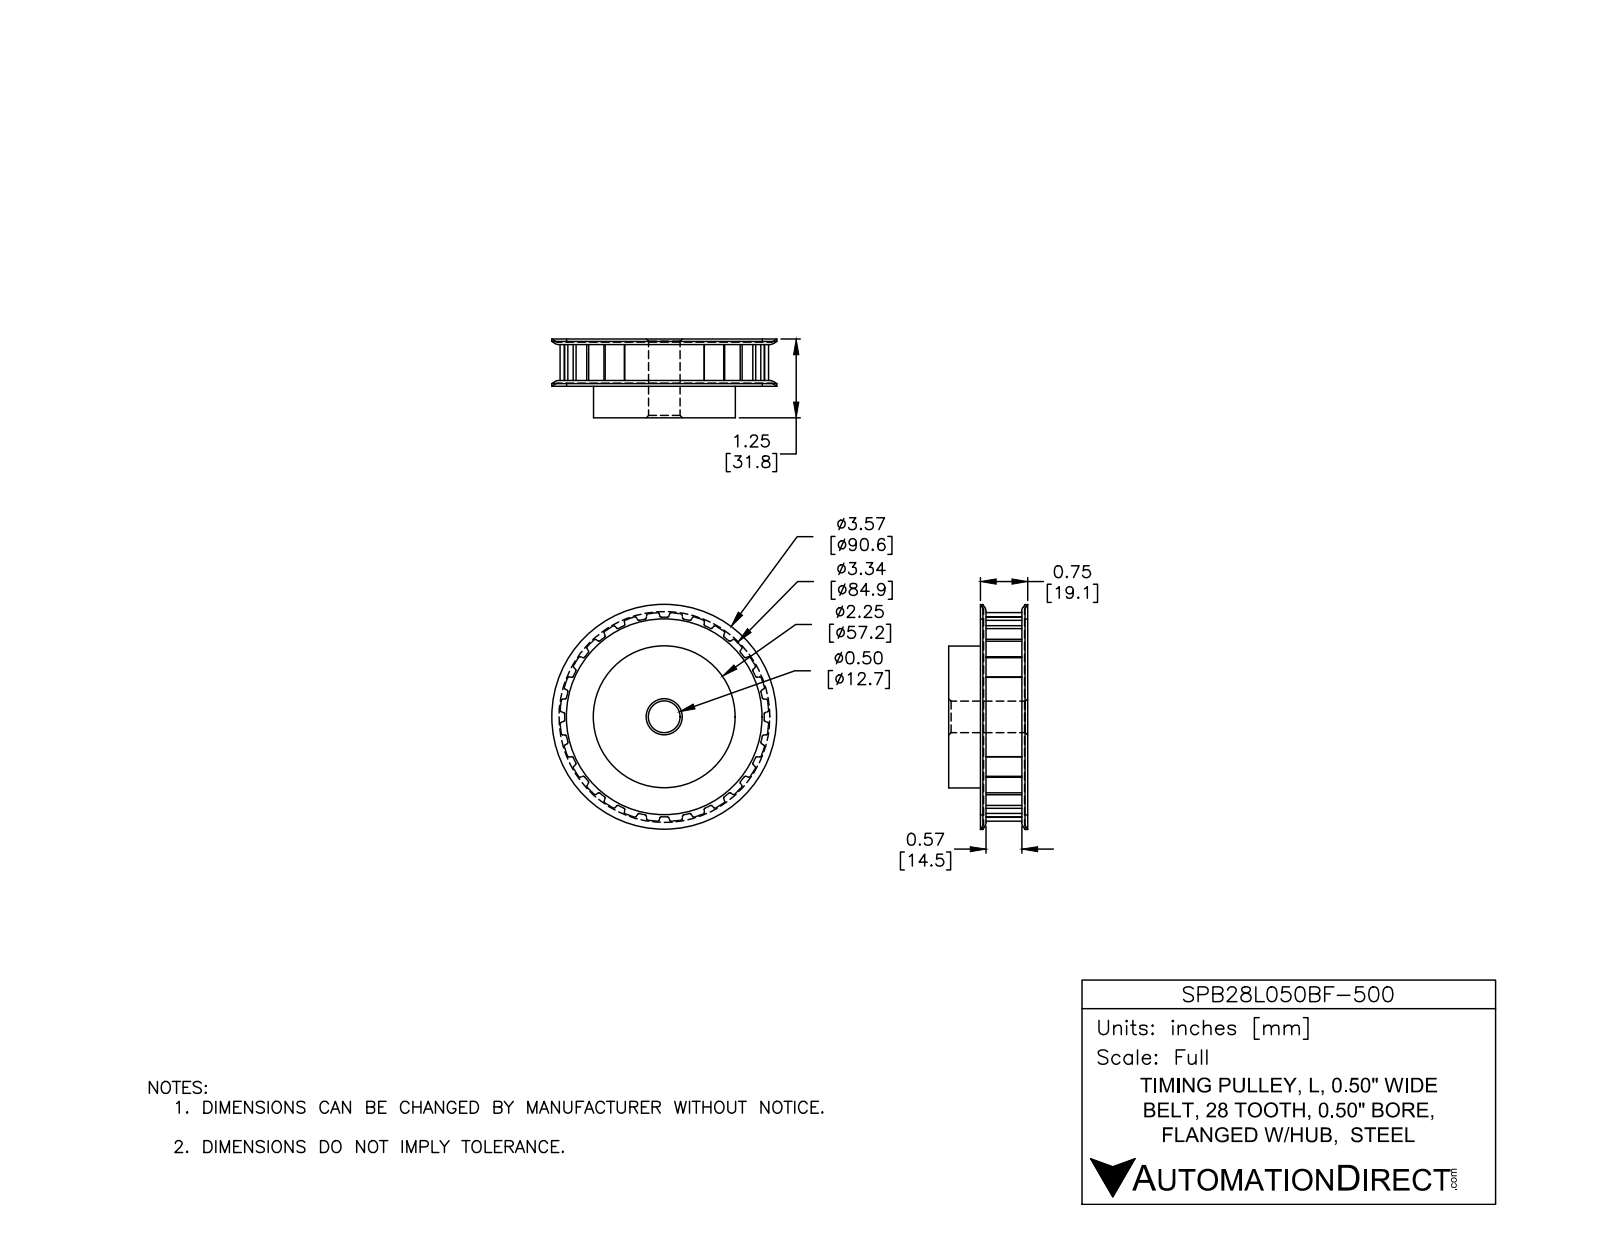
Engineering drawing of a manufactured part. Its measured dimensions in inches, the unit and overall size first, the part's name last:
Units: inches
Overall size (bounding box): 3.566 × 3.566 × 1.25
Round holes (diameter × count): ⌀0.5 ×1
Round bosses / shafts (diameter × count): ⌀3.566 ×1, ⌀3.102 ×1, ⌀2.25 ×1
Partial cylindrical surfaces — rounded edges, fillets, slot ends (radius × count): R0.02 ×112, R1.656 ×1
Main face-to-face distances: 1.25, 0.75, 0.5, 0.05, 0.7, 0.65, 1.2, 0.55, 0.09, 0.66
Volume: 8.02 in³ · Surface area: 38.18 in²
Bodies: 1 solid, 281 faces (91 planar, 174 cylindrical, 16 other)
Part name (STEP PRODUCT): SPB28L050BF-500
STEP written by: SolidWorks 2015 (AUTOMOTIVE_DESIGN)
